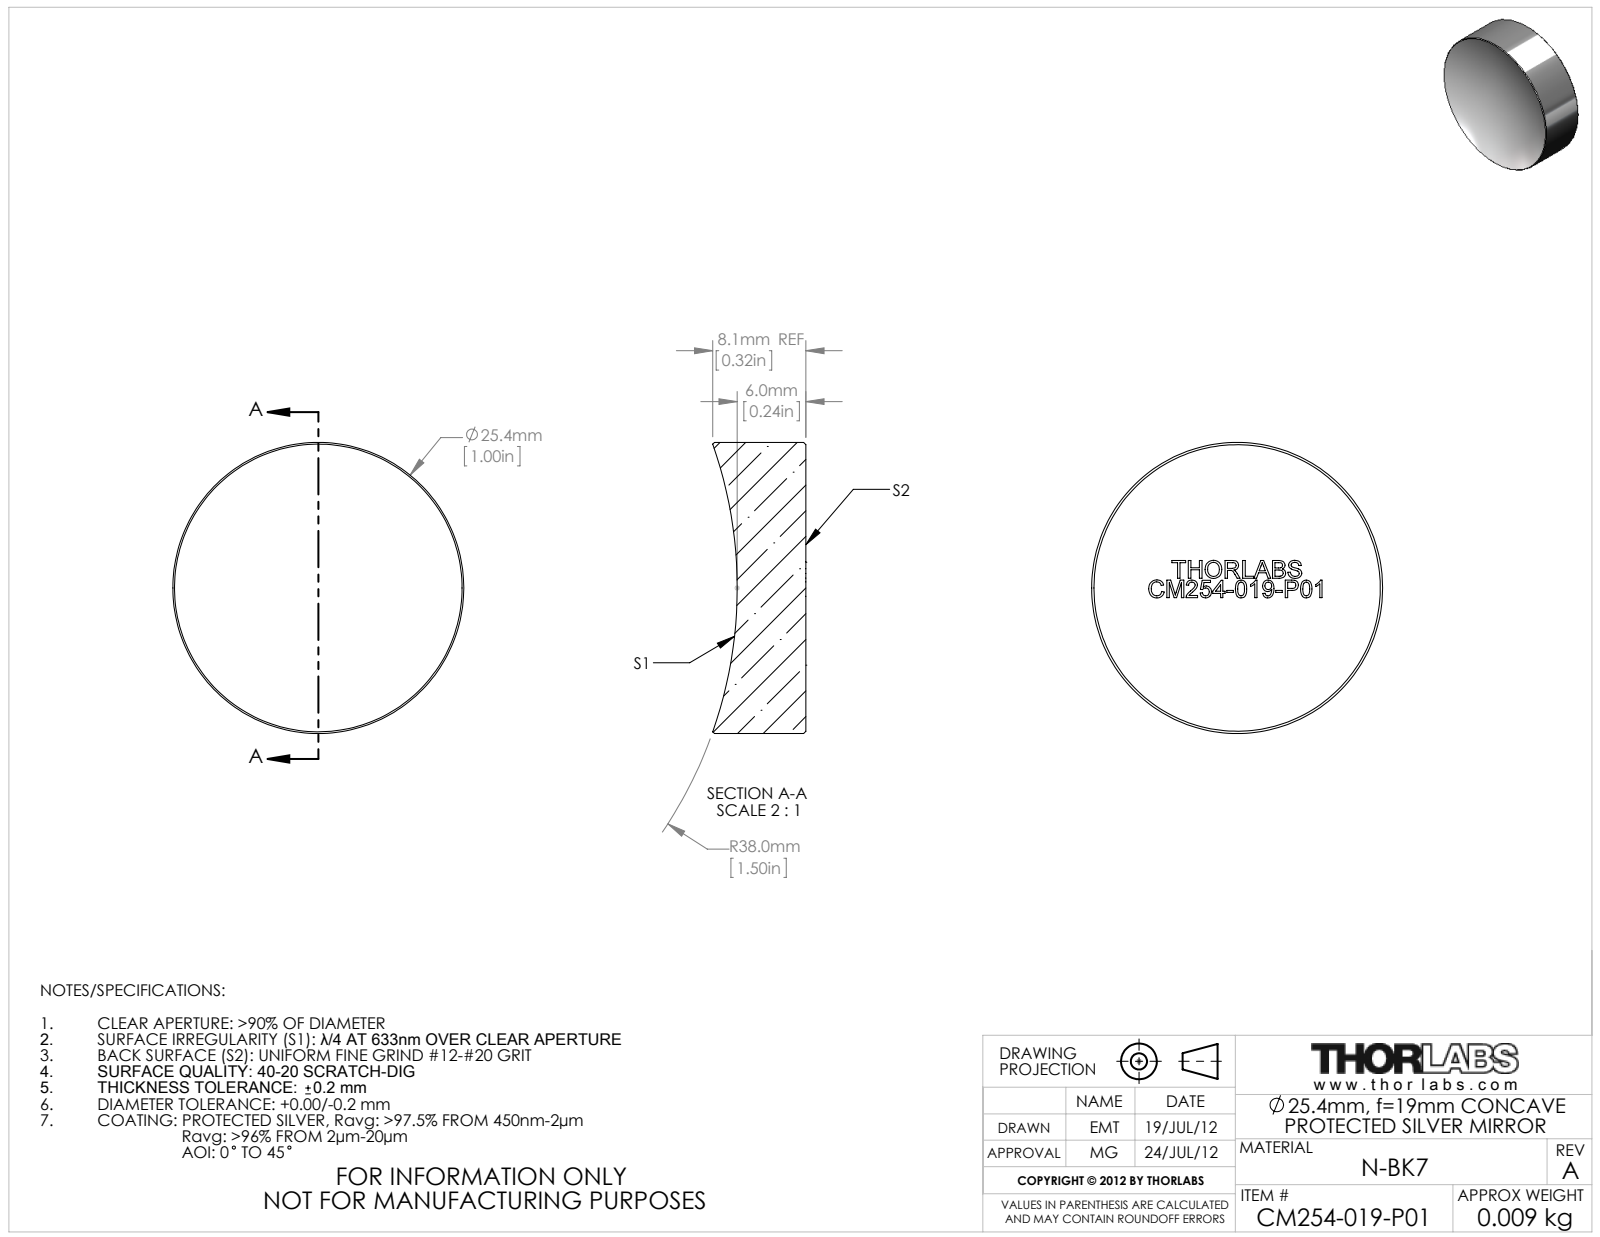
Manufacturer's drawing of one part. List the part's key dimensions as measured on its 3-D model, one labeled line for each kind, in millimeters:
Part name (STEP PRODUCT): 24632-E0W
STEP written by: SolidWorks 2011 (CONFIG_CONTROL_DESIGN)
Units: millimetres
Bodies: 0 solids, 40 faces (32 planar, 2 cylindrical, 6 other)
Overall size (bounding box): 25.4 × 25.4 × 8.1
Round bosses / shafts (diameter × count): ⌀25.4 ×1
